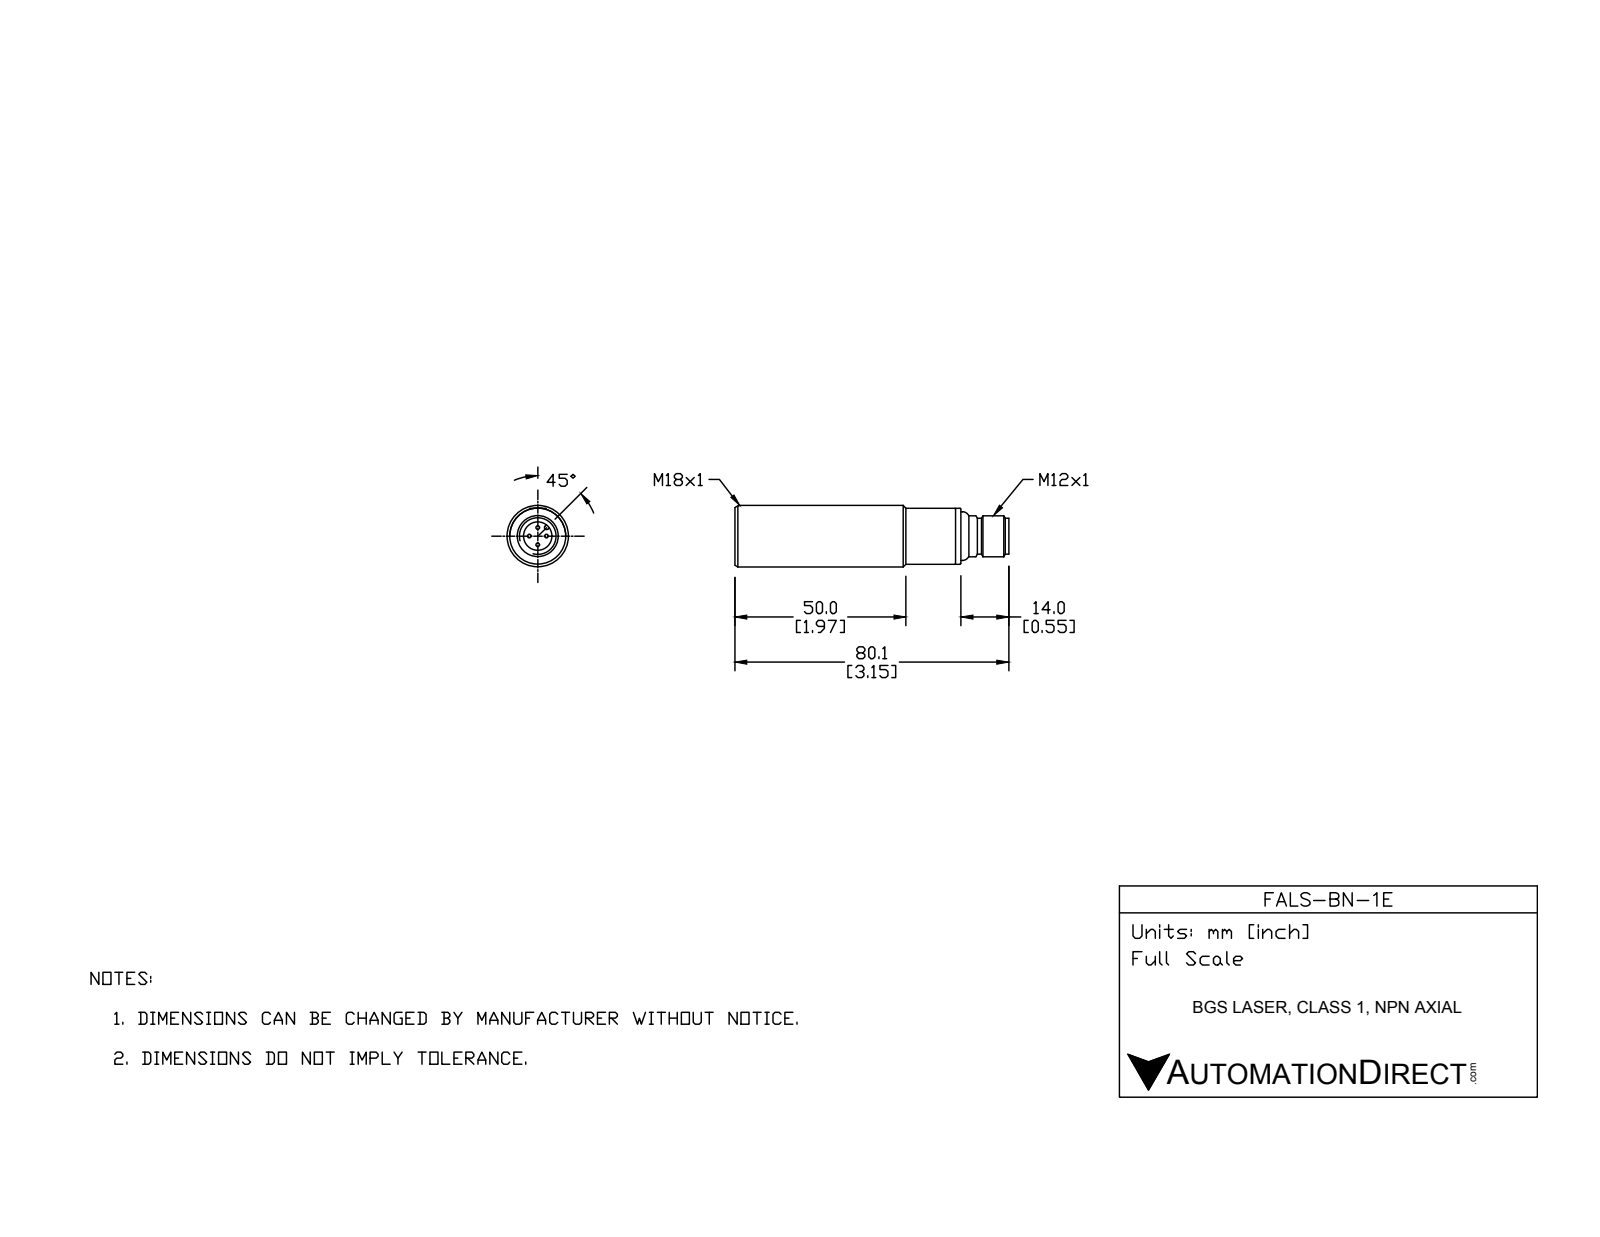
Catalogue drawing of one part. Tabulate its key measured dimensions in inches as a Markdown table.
| quantity | value |
| --- | --- |
| part name | FALS-BN-1E |
| STEP written by | SolidWorks 2017 (AUTOMOTIVE_DESIGN) |
| units | inches |
| bodies | 10 solids, 166 faces (50 planar, 73 cylindrical, 43 other) |
| overall size | 3.154 × 0.709 × 0.709 |
| volume | 1.039 in³ |
| surface area | 10.09 in² |
| round holes (diameter × count) | 0.039 × 4, 0.043 × 4, 0.106 × 1, 0.185 × 1, 0.278 × 1, 0.327 × 1, 0.622 × 1 |
| round bosses / shafts (diameter × count) | 0.709 × 1, 0.646 × 1, 0.559 × 1, 0.472 × 1, 0.413 × 1, 0.276 × 1, 0.189 × 1 |
| partial cylindrical surfaces (radius × count) | 0.02 × 4, 0.024 × 1, 0.331 × 1 |
| main face-to-face distances | 0.063, 2.531, 0.055, 2.476, 2.469, 2.539, 2.594, 2.795, 2.74, 2.732 |
| hole center spacings | 0.098, 0.139, 0.197 |
